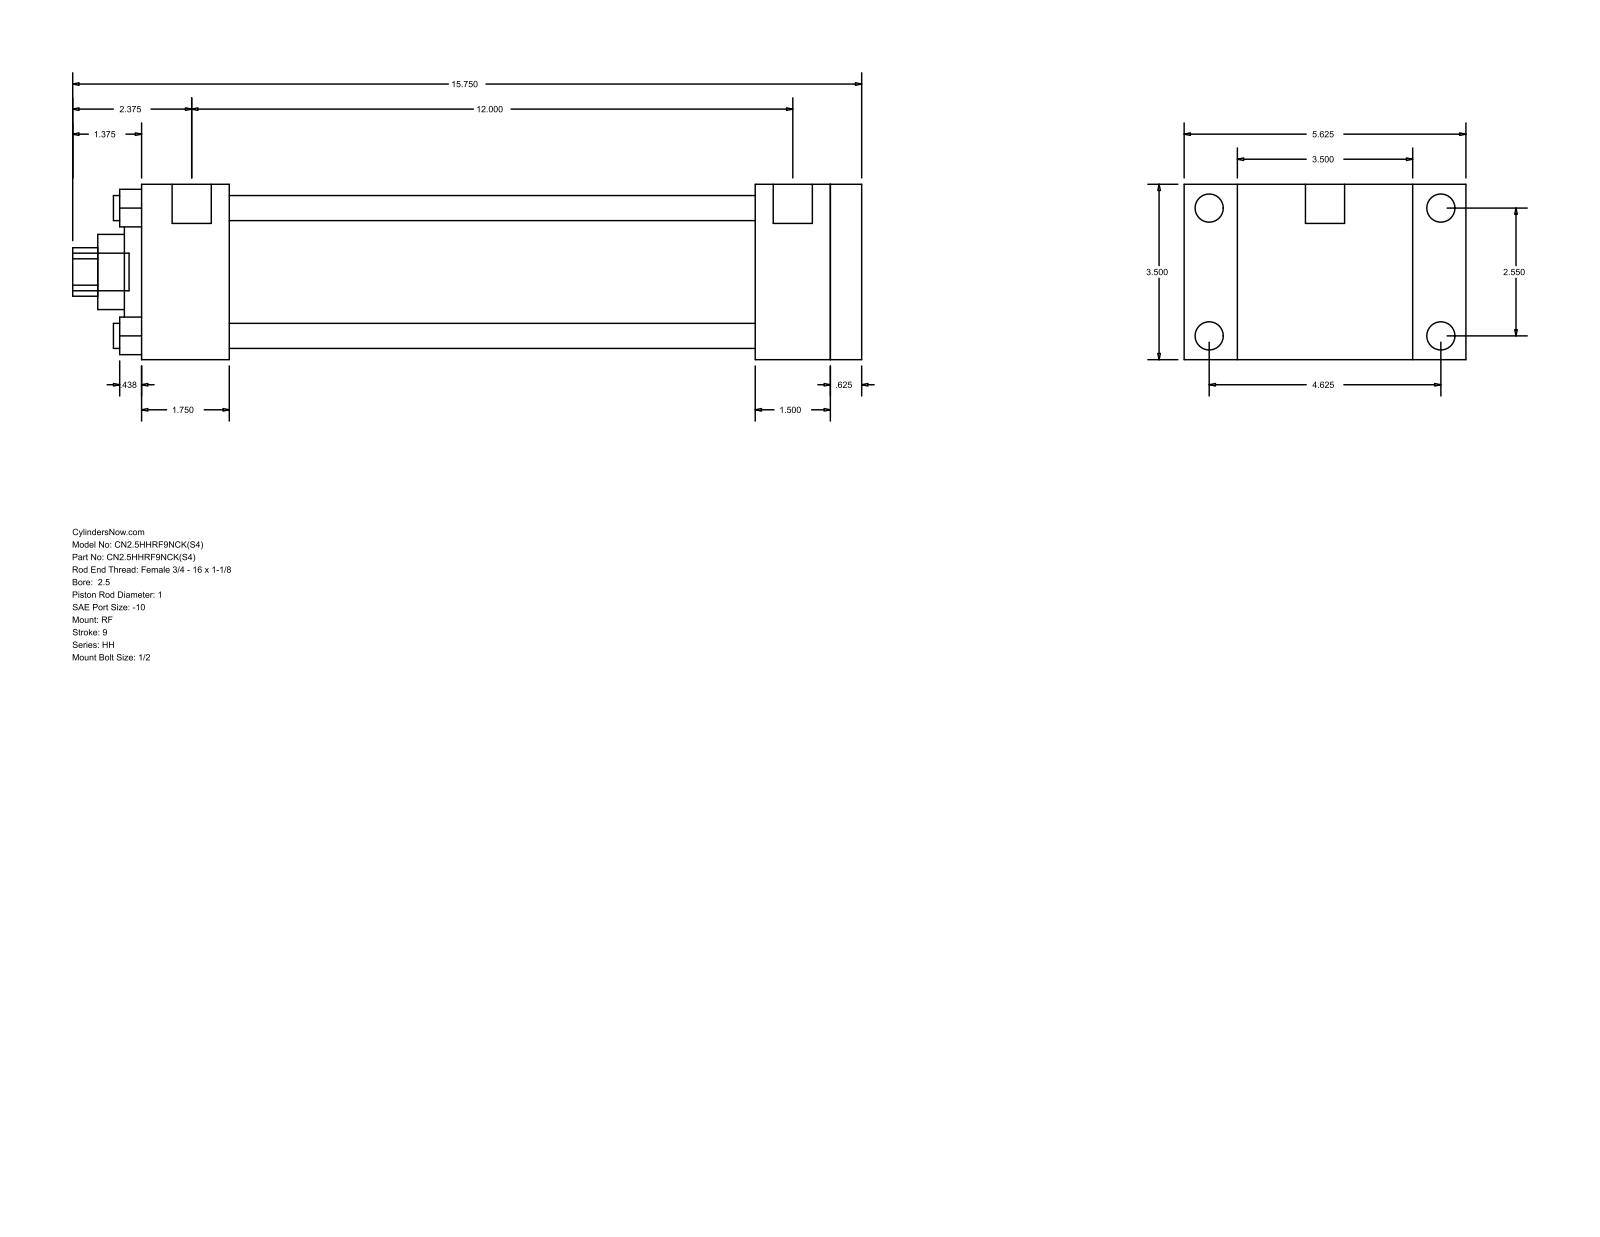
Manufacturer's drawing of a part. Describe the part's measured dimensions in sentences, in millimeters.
The part is named "HH_RF__0250_1". Its 3-D file was written by "GSSL Pune (CONFIG_CONTROL_DESIGN)". It is 0 solids with 94 faces: 65 planar, 29 cylindrical and 0 other. Overall it measures 400.05 by 142.88 by 88.9 millimeters. Round holes: 4 of diameter 12.7, 1 of diameter 25.4, 1 of diameter 38.1, 1 of diameter 60.33, 1 of diameter 73.03. Round bosses or shafts: 4 of diameter 14.3, 4 of diameter 5.56, 2 of diameter 19.84, 1 of diameter 19.05. Partial cylindrical surfaces (rounded edges, fillets, slot ends): 1 of radius 12.29. The main face-to-face distances are 88.9, 15.87, 349.26, 365.13, 44.46, 304.8, 320.67, 311.15, 266.69, 38.11. The hole center spacings are 45.79, 64.76, 91.58.
